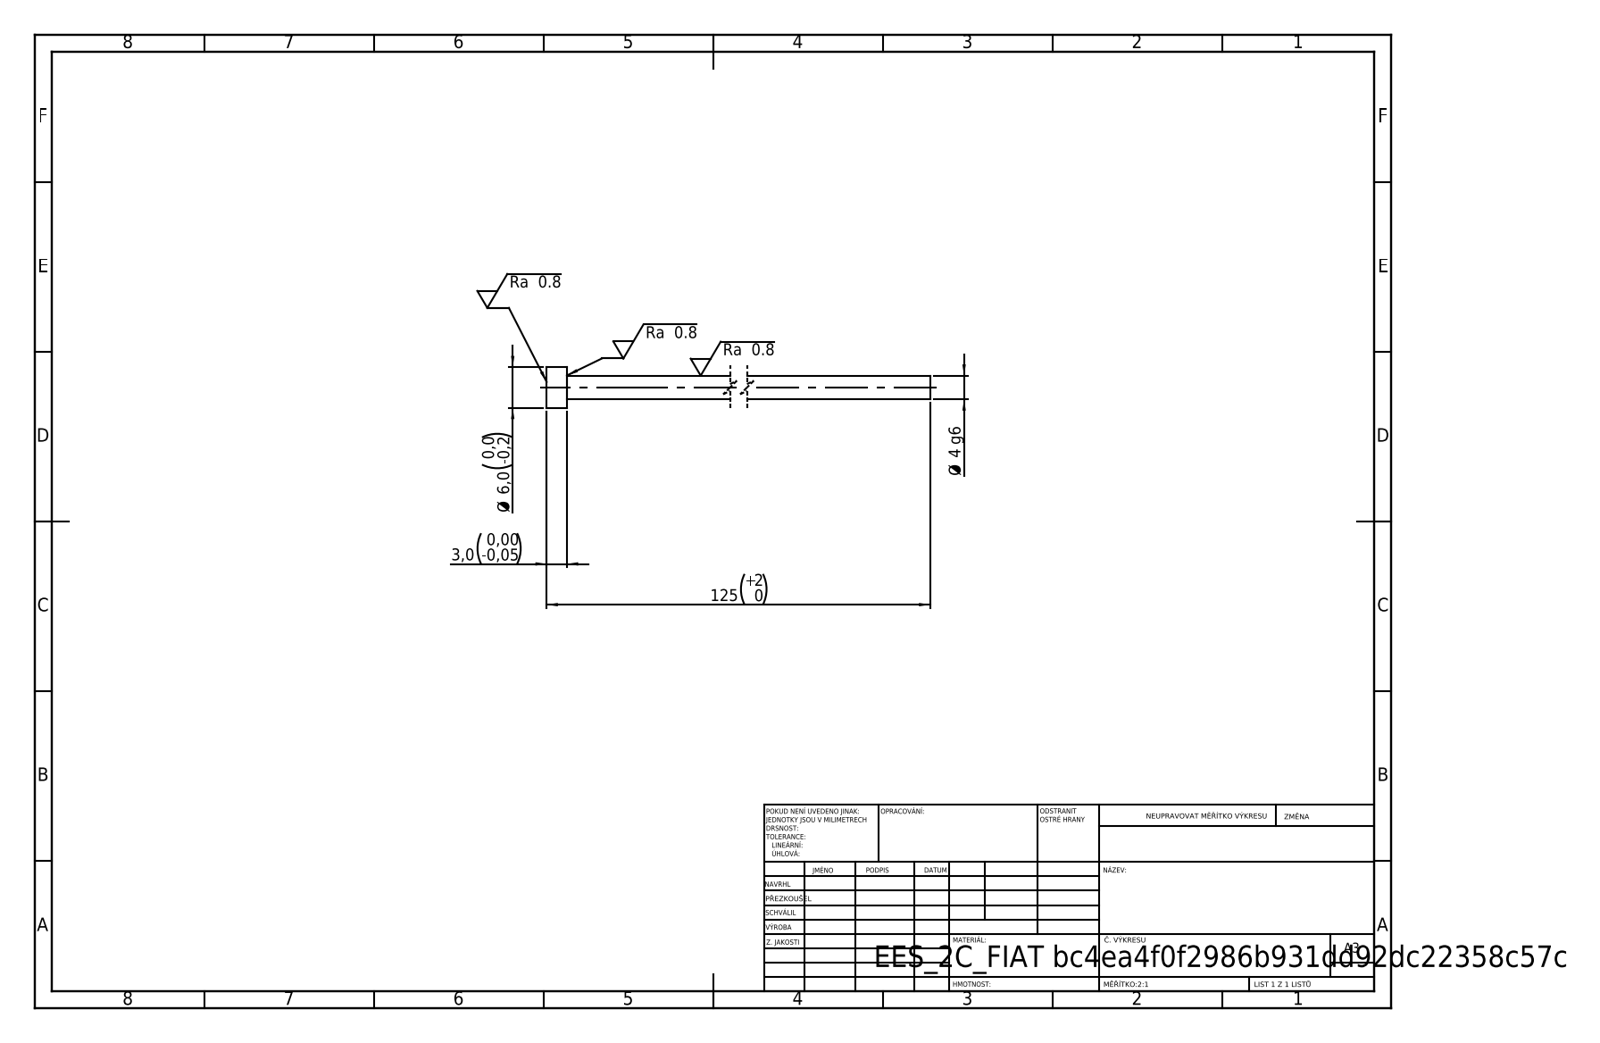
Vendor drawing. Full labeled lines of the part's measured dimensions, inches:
STEP written by: SolidWorks 2019 (CONFIG_CONTROL_DESIGN)
Units: inches
Bodies: 1 solid, 7 faces (3 planar, 4 cylindrical, 0 other)
Overall size (bounding box): 4.921 × 0.236 × 0.236
Volume: 0.077 in³ · Surface area: 2.255 in²
Round bosses / shafts (diameter × count): ⌀0.236 ×1, ⌀0.138 ×1
Main face-to-face distances: 0.118, 4.921, 4.803
